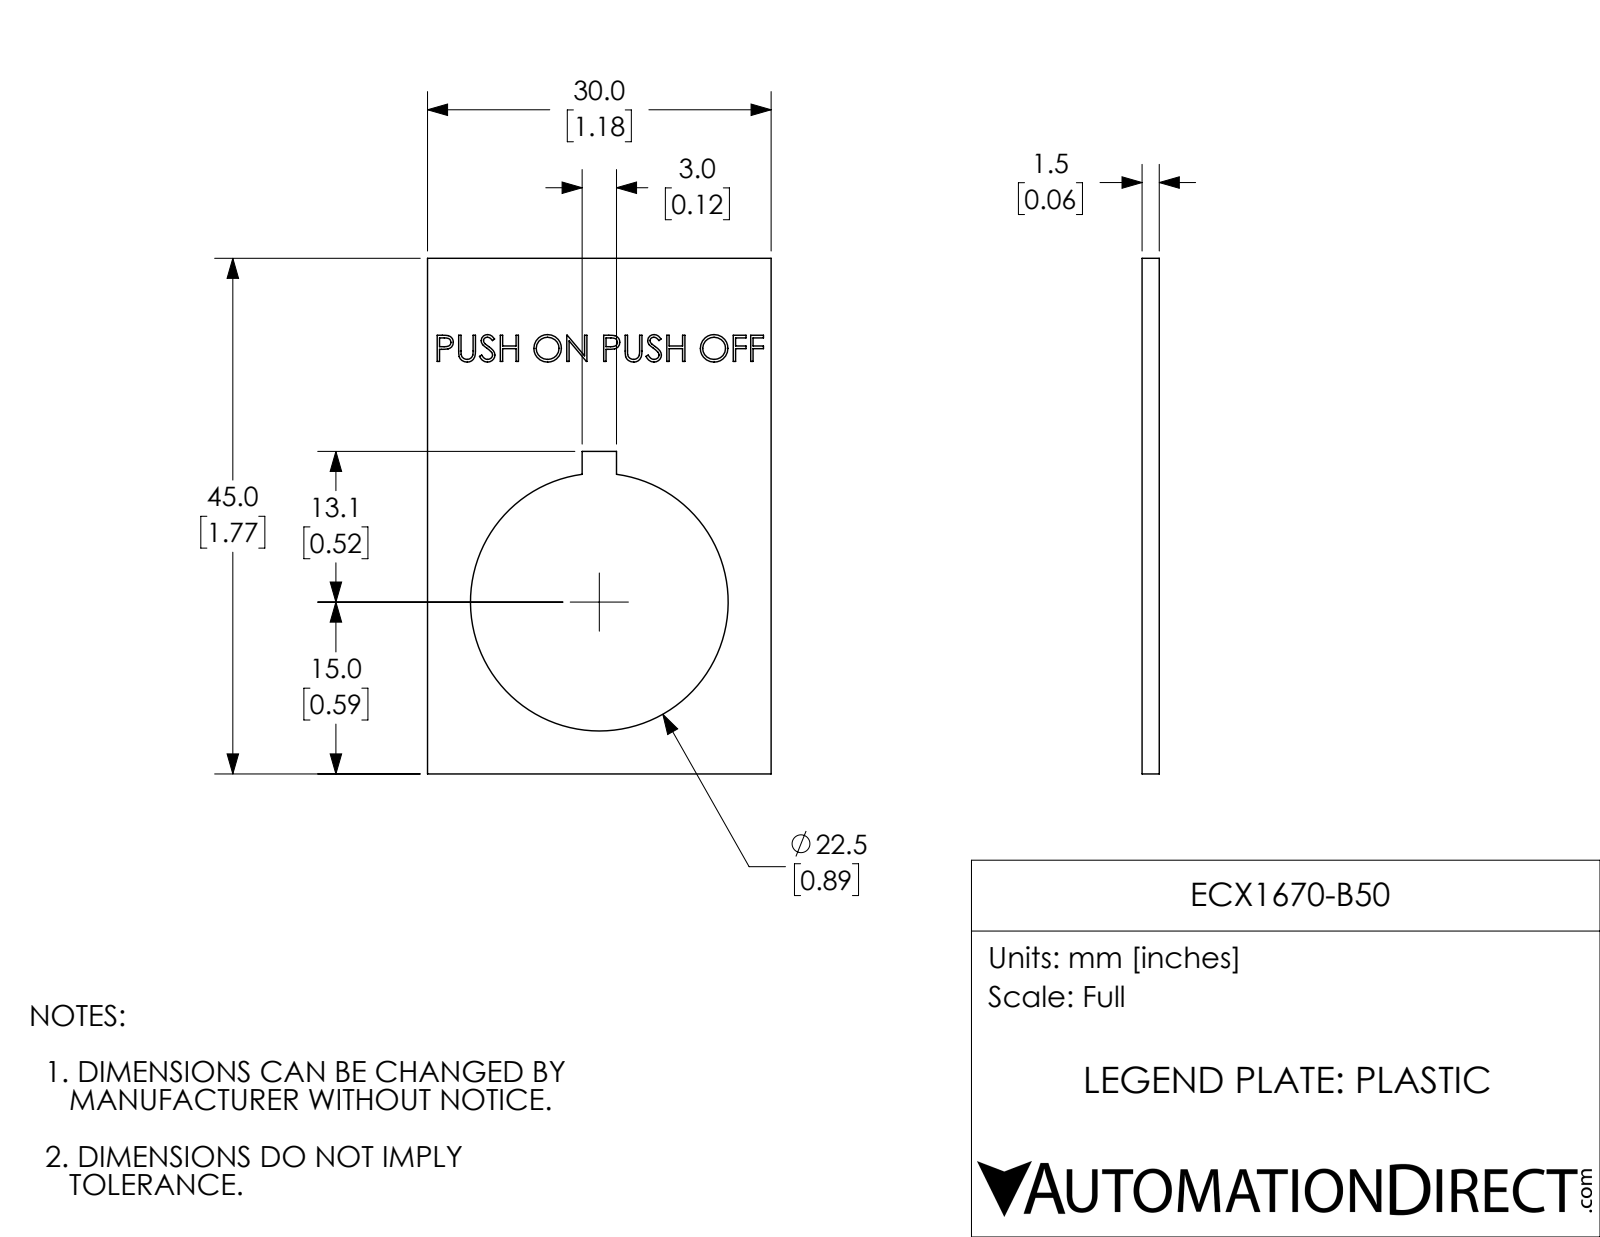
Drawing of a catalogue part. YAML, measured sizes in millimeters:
part_name: "ECX1670-B50"
step_written_by: "SolidWorks 2017 (AUTOMOTIVE_DESIGN)"
units: millimeters
bodies: {solids: 1, faces: 187, planar: 112, cylindrical: 3, other: 72}
overall_size: [45, 30, 1.5]
volume: 1400
surface_area: 2234
round_holes:
  - {diameter: 22.5, count: 1}
face_to_face_distances: [1.5, 30, 45, 1.5, 13.5, 16.5, 28.1, 16.8, 3, 14.5]
